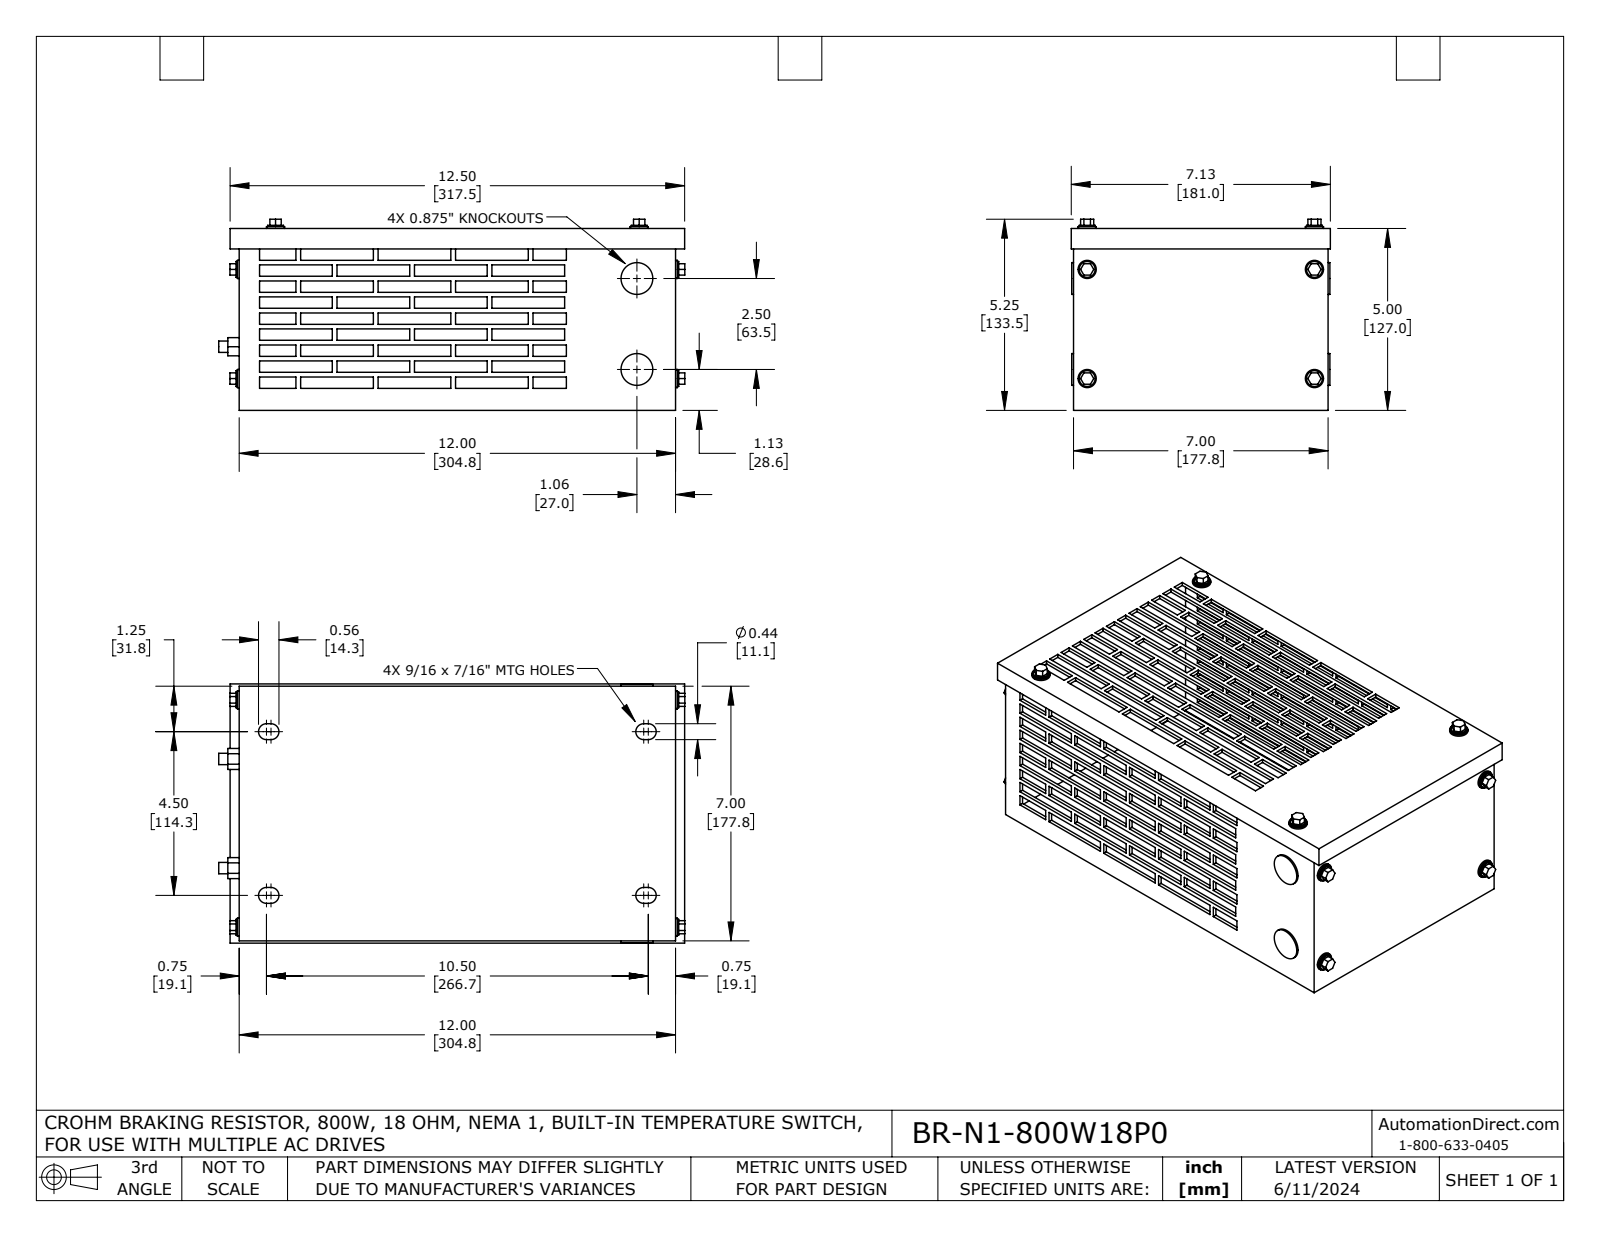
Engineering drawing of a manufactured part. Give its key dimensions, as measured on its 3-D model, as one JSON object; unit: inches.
{"part_name": "BR-N1-800W18P0", "step_written_by": "SolidWorks 2021 (AUTOMOTIVE_DESIGN)", "units": "inches", "bodies": {"solids": 31, "faces": 846, "planar": 746, "cylindrical": 100, "other": 0}, "overall_size": [12.817, 7.125, 5.254], "volume_in3": 28.59, "surface_area_in2": 639.2, "round_holes": [[0.25, 8], [0.75, 2]], "round_bosses_or_shafts": [[0.5, 8], [0.437, 8], [0.875, 2], [0.313, 2]], "partial_cylinders_radius": [[0.219, 8]], "face_to_face_distances": [0.1, 4.9, 11.9, 6.9, 5, 4.8, 12, 7, 11.8, 6.8], "hole_center_spacings": [6.25, 3, 6.933, 10, 11.793, 2.5]}
